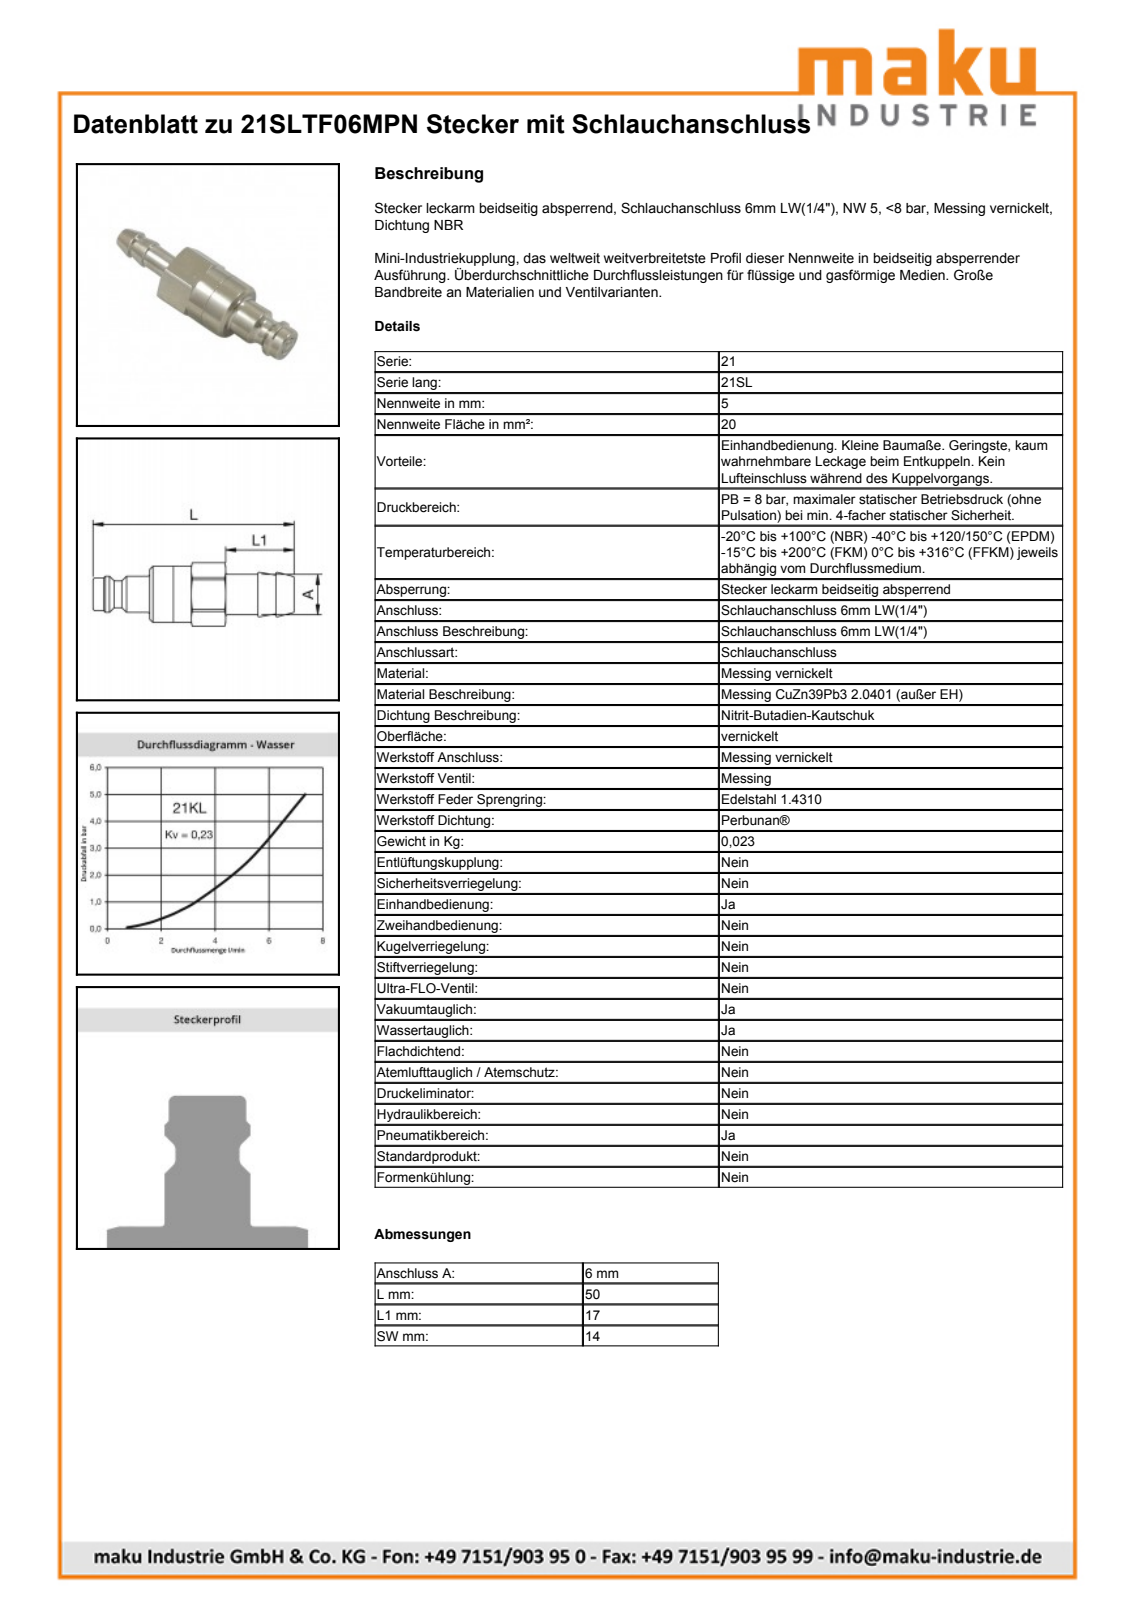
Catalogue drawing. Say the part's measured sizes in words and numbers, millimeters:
The part is named "D113604". Its 3-D file was written by "Autodesk Inventor 2013 (AUTOMOTIVE_DESIGN)". It is 1 solid with 61 faces: 14 planar, 16 cylindrical and 31 other. Overall it measures 50 by 15.8 by 14 millimeters. Its volume is 4 254 cubic millimeters and its surface area 2 333 square millimeters. Round holes: 1 of diameter 12. Round bosses or shafts: 1 of diameter 14, 1 of diameter 11.98, 1 of diameter 11, 1 of diameter 10.67, 1 of diameter 9, 1 of diameter 8.1, 1 of diameter 6.65, 1 of diameter 6.05. Partial cylindrical surfaces (rounded edges, fillets, slot ends): 1 of radius 7.9. The main face-to-face distances are 14, 18.9, 14.1, 33, 17, 9, 50, 35.9, 4.5, 24.
